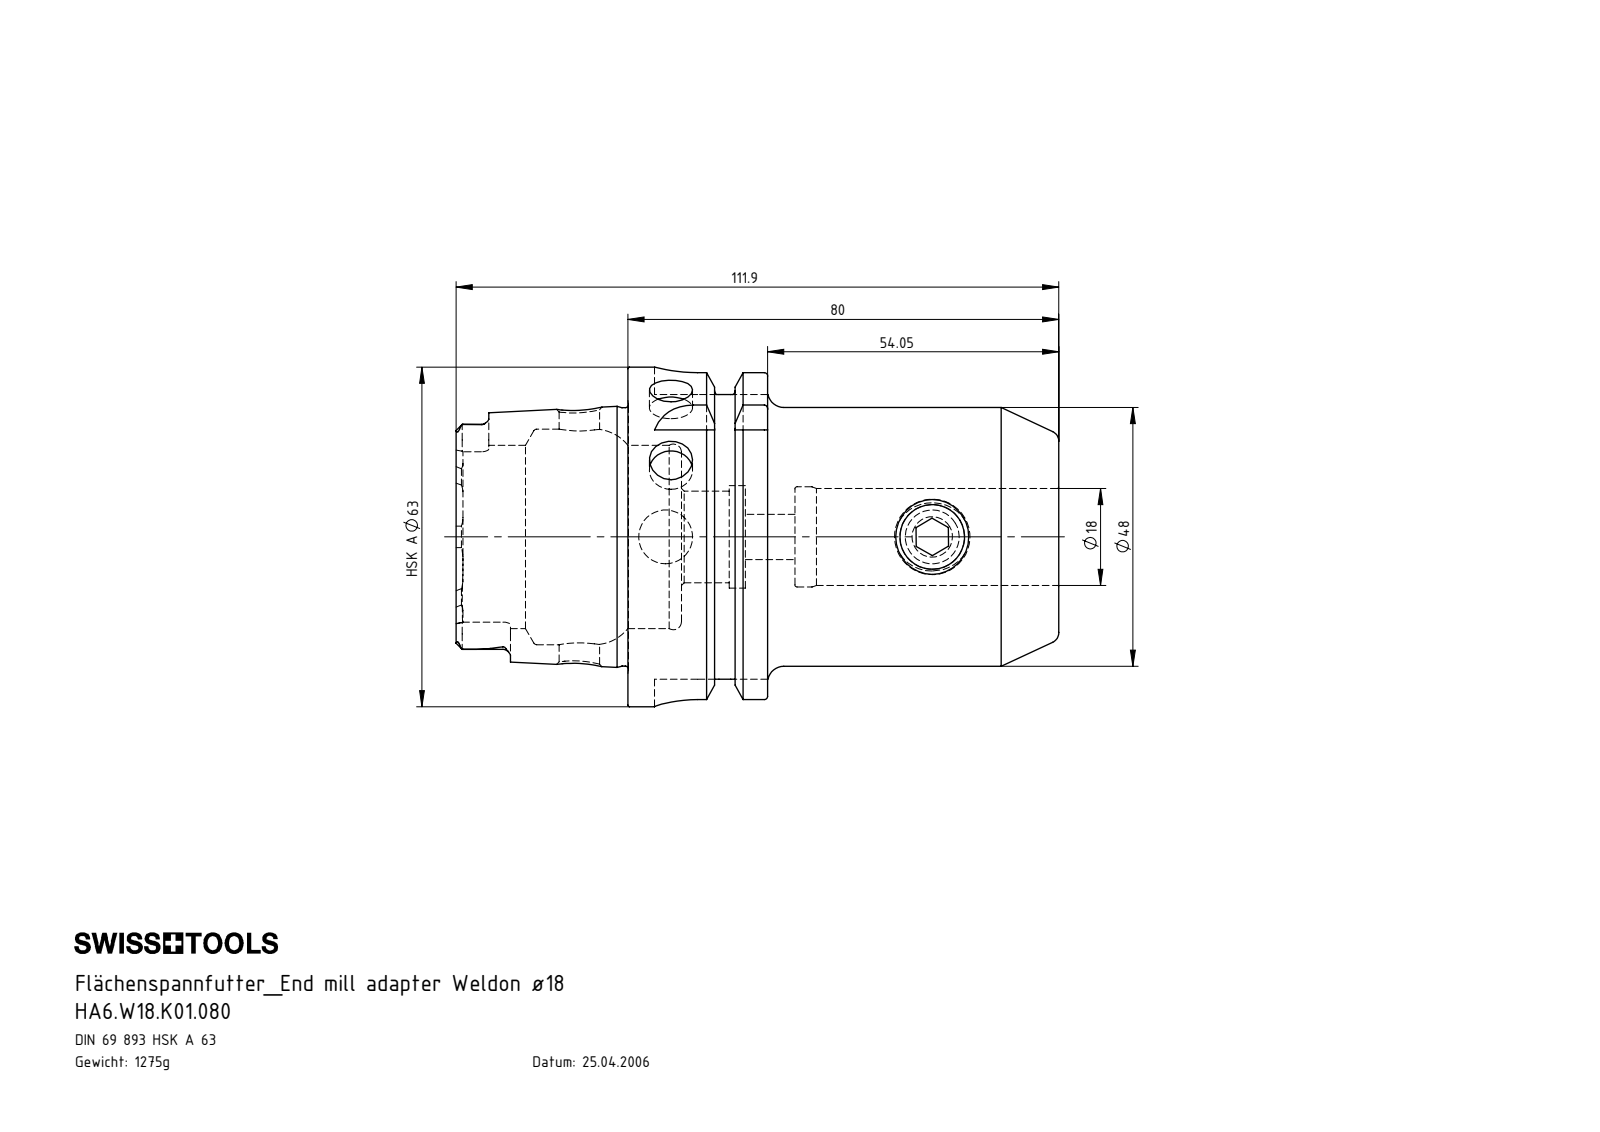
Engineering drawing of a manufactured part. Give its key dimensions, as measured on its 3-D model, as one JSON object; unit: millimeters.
{"part_name": "HA6-W18.K01.080; W16-ER1.001.016; HA6-W18.K01.080_B_Fertigbearbeitung", "step_written_by": "SolidWorks 2012 (AUTOMOTIVE_DESIGN)", "units": "millimeters", "bodies": {"solids": 2, "faces": 209, "planar": 59, "cylindrical": 57, "other": 93}, "overall_size": [111.9, 63, 63], "volume_mm3": 162449, "surface_area_mm2": 34056, "round_holes": [[8, 2], [7.5, 1], [8.4, 1], [10, 1], [12, 1], [17, 1], [18, 1], [18.6, 1], [19, 1], [34, 1], [40, 1]], "round_bosses_or_shafts": [[63, 1], [54.95, 1], [48, 1], [47.94, 1], [14, 1]], "partial_cylinders_radius": [[1.4, 6], [2.88, 4], [8, 4]], "face_to_face_distances": [80, 25.95, 54.05, 16, 9.95, 70.05, 52.8, 31.9, 41.85, 57.85], "hole_center_spacings": [49.5]}
